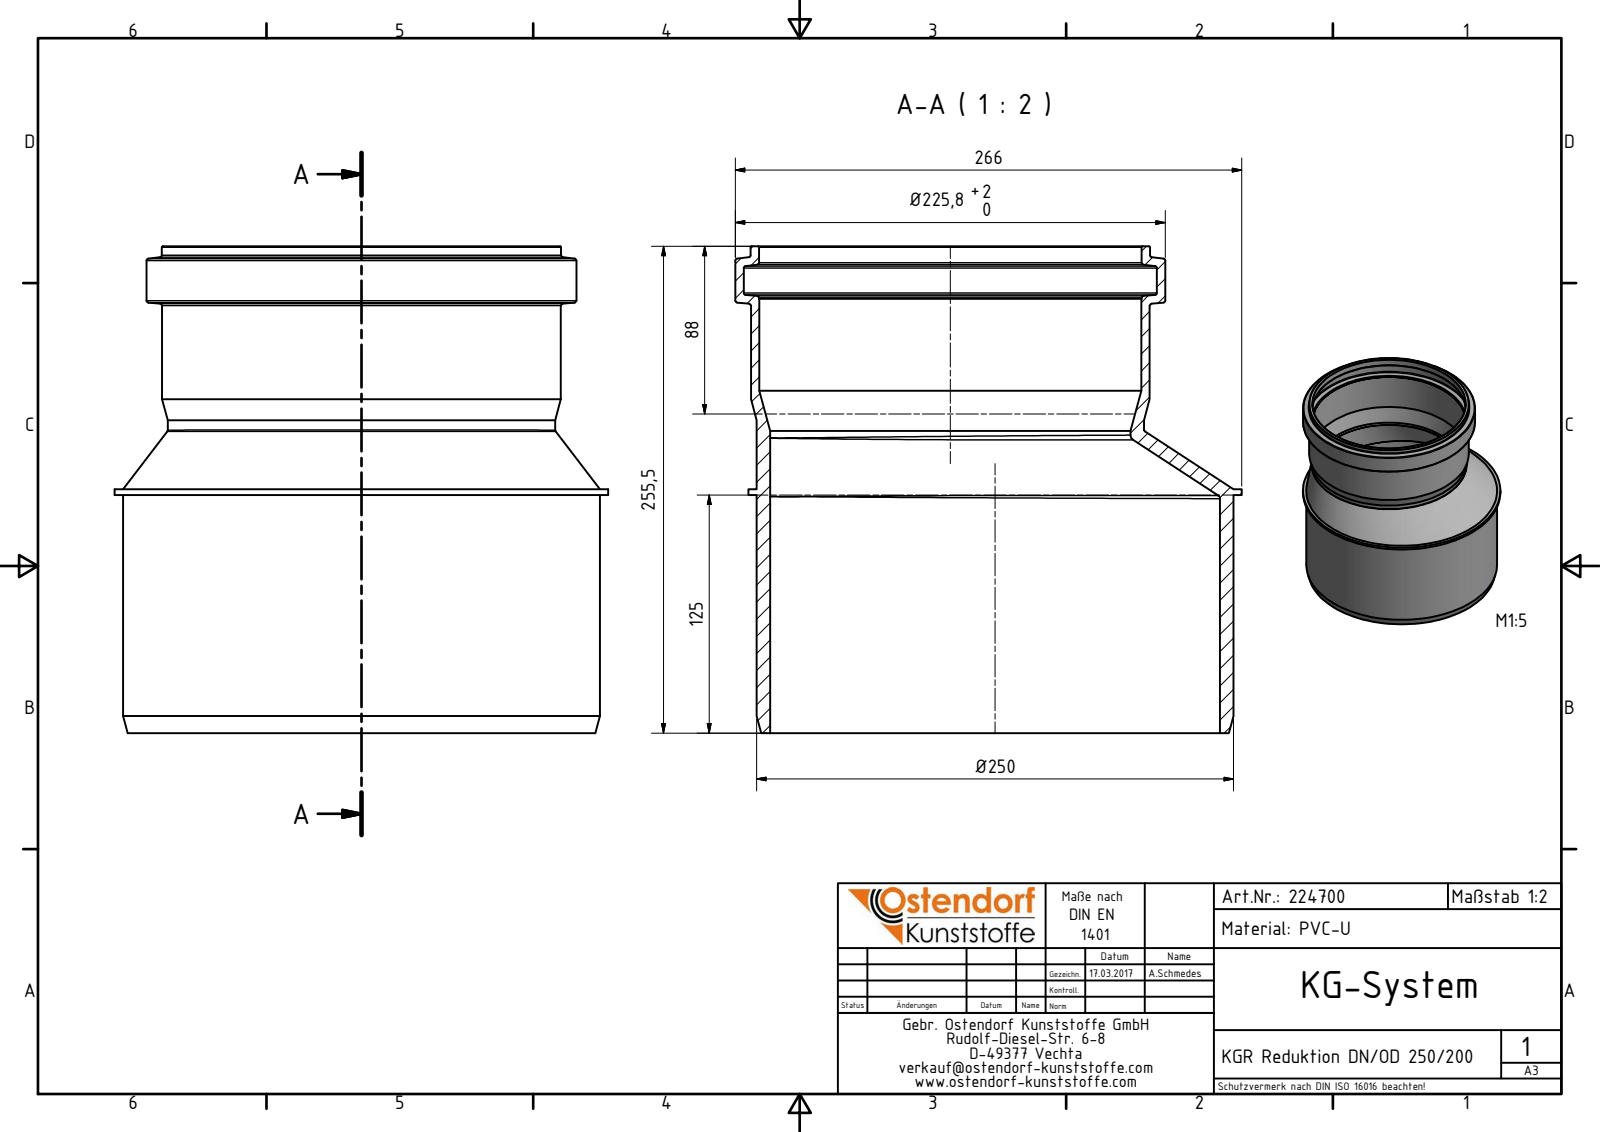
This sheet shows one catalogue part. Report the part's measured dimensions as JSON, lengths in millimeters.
{"part_name": "224700 KGR Reduktion DN_OD 250_200", "step_written_by": "Autodesk Inventor 2016 (AUTOMOTIVE_DESIGN)", "units": "millimeters", "bodies": {"solids": 1, "faces": 39, "planar": 5, "cylindrical": 12, "other": 22}, "overall_size": [266, 259.2, 255.5], "volume_mm3": 1245000, "surface_area_mm2": 409752, "round_holes": [[189.3, 1], [200.6, 1], [200.9, 1], [217, 1], [236.3, 1]], "round_bosses_or_shafts": [[259.2, 1], [250.5, 1], [225.8, 1], [209.7, 1], [209.4, 1], [203.5, 1]], "face_to_face_distances": [125, 128, 3, 255.5, 130.5, 127.5, 227.93, 102.93, 99.93, 27.57], "hole_center_spacings": [23.5]}
